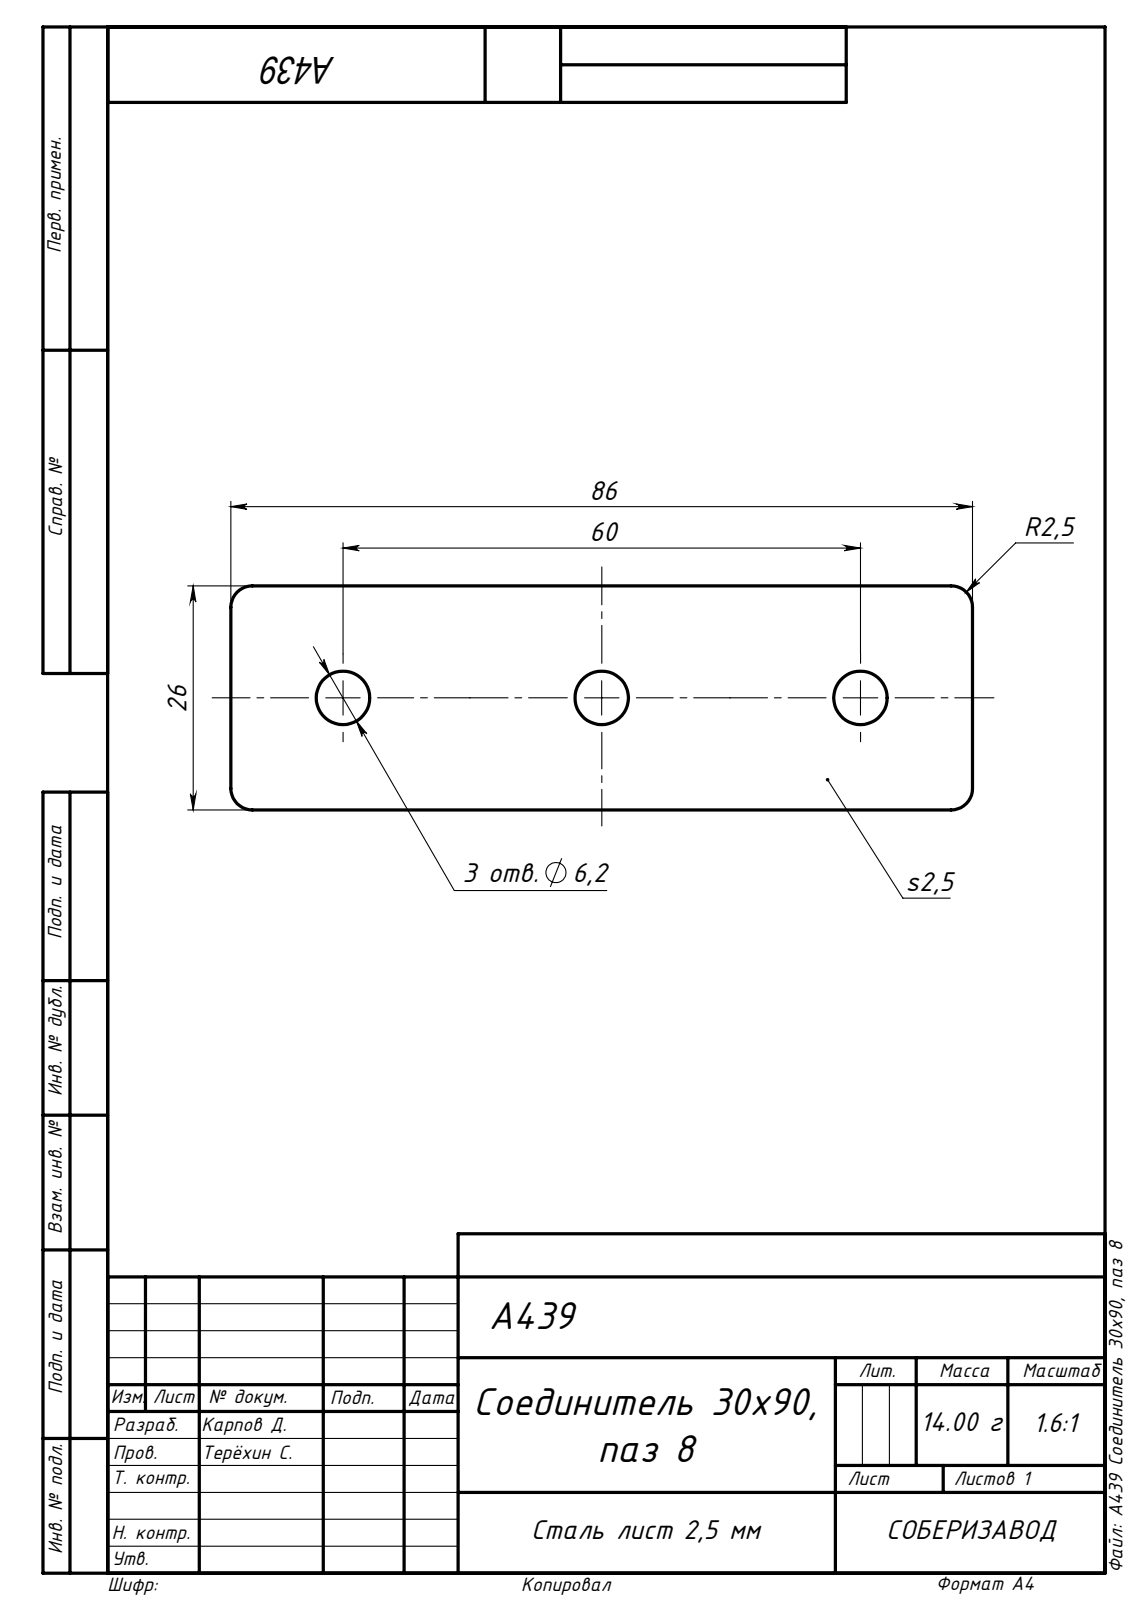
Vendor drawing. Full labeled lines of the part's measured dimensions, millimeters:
STEP written by: SolidWorks 2020 (AUTOMOTIVE_DESIGN)
Units: millimetres
Bodies: 1 solid, 16 faces (6 planar, 10 cylindrical, 0 other)
Overall size (bounding box): 86 × 26 × 2.5
Volume: 5 350 mm³ · Surface area: 4 975 mm²
Round holes (diameter × count): ⌀6.2 ×3
Partial cylindrical surfaces — rounded edges, fillets, slot ends (radius × count): R2.5 ×4
Main face-to-face distances: 2.5, 26, 86
Hole centre spacings: 30, 60
